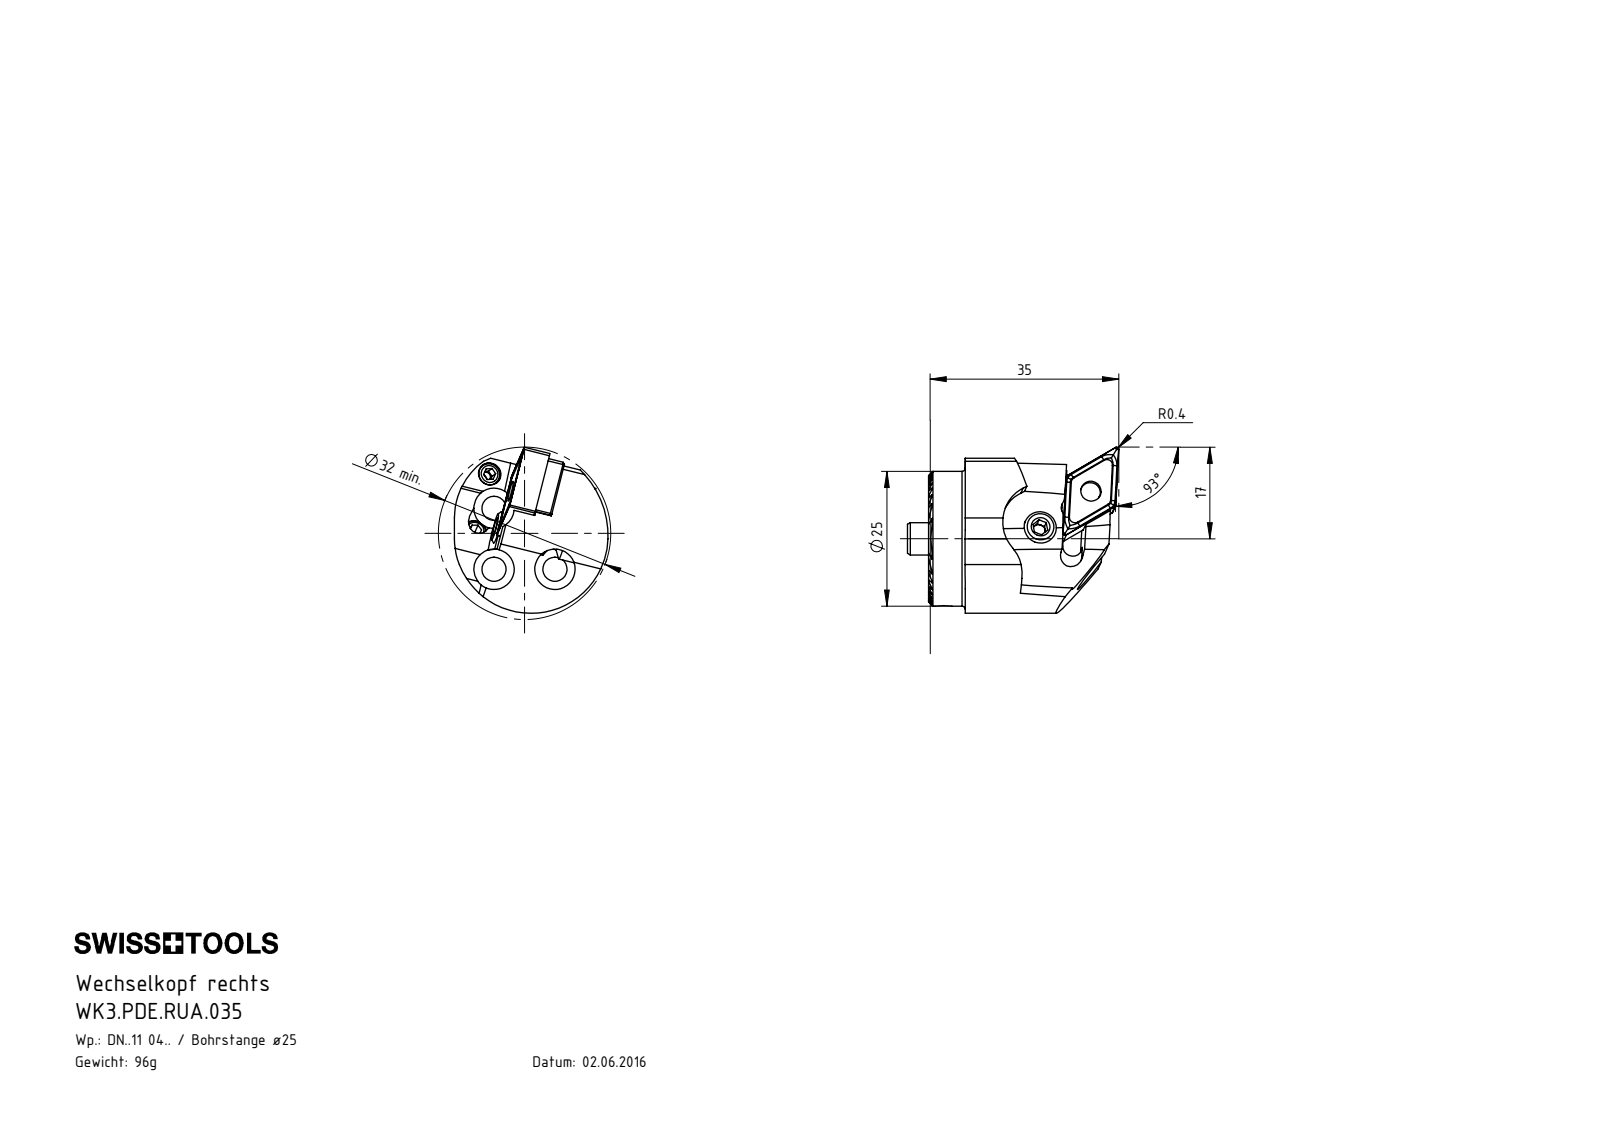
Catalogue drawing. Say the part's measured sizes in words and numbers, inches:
The part is named "WDE-ER3.101.000_A; DNMG110404; WDE-ER2.101.003_A; WK3-ER1.001.006_A_Fertigbearbeitung (+6 more)". Its 3-D file was written by "SolidWorks 2017 (AUTOMOTIVE_DESIGN)". It is 15 solids with 458 faces: 238 planar, 104 cylindrical and 116 other. Overall it measures 1.544 by 1.214 by 1.122 inches. Its volume is 0.771 cubic inches and its surface area 13.58 square inches. Round holes: 3 of diameter 0.094, 3 of diameter 0.098, 3 of diameter 0.118, 3 of diameter 0.165, 3 of diameter 0.177, 3 of diameter 0.295, 2 of diameter 0.067, 2 of diameter 0.13, 1 of diameter 0.15, 1 of diameter 0.189, 1 of diameter 0.197, 1 of diameter 0.236. Round bosses or shafts: 3 of diameter 0.118, 2 of diameter 0.157, 1 of diameter 0.984, 1 of diameter 0.236, 1 of diameter 0.232, 1 of diameter 0.113. Partial cylindrical surfaces (rounded edges, fillets, slot ends): 20 of radius 0.005, 8 of radius 0.016, 5 of radius 0.083, 2 of radius 0.276, 2 of radius 0.512, 1 of radius 0.072, 1 of radius 0.073, 1 of radius 0.089. The main face-to-face distances are 0.17, 0.043, 0.128, 0.341, 0.213, 0.298, 0.085, 0.085, 0.021, 0.383. The hole center spacings are 0.315, 0.446, 0.464, 0.464, 0.63.
